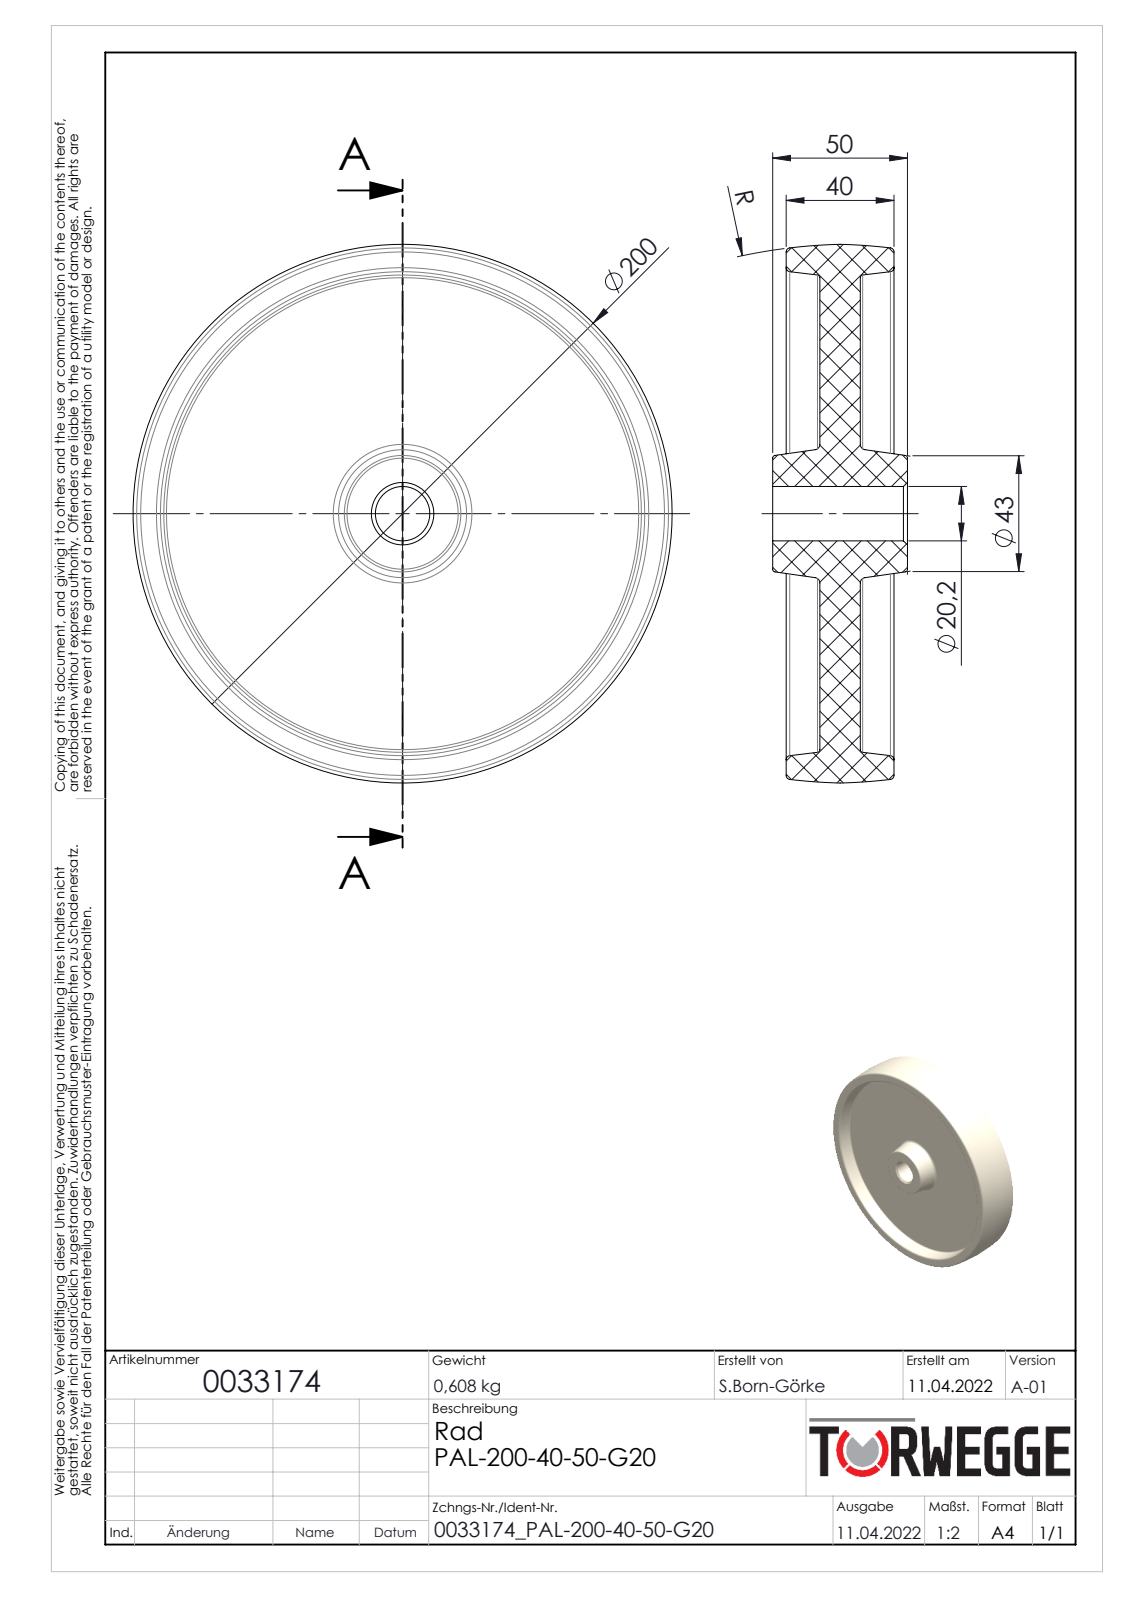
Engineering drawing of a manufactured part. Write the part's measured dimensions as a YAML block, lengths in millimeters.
part_name: "0033174"
step_written_by: "SolidWorks 2020 (AUTOMOTIVE_DESIGN)"
units: millimeters
bodies: {solids: 1, faces: 42, planar: 6, cylindrical: 2, other: 34}
overall_size: [200, 200, 50]
volume: 656786
surface_area: 103515
round_holes:
  - {diameter: 20.2, count: 1}
face_to_face_distances: [15, 12.5, 27.5, 40, 5, 17.5, 32.5, 45, 50]
